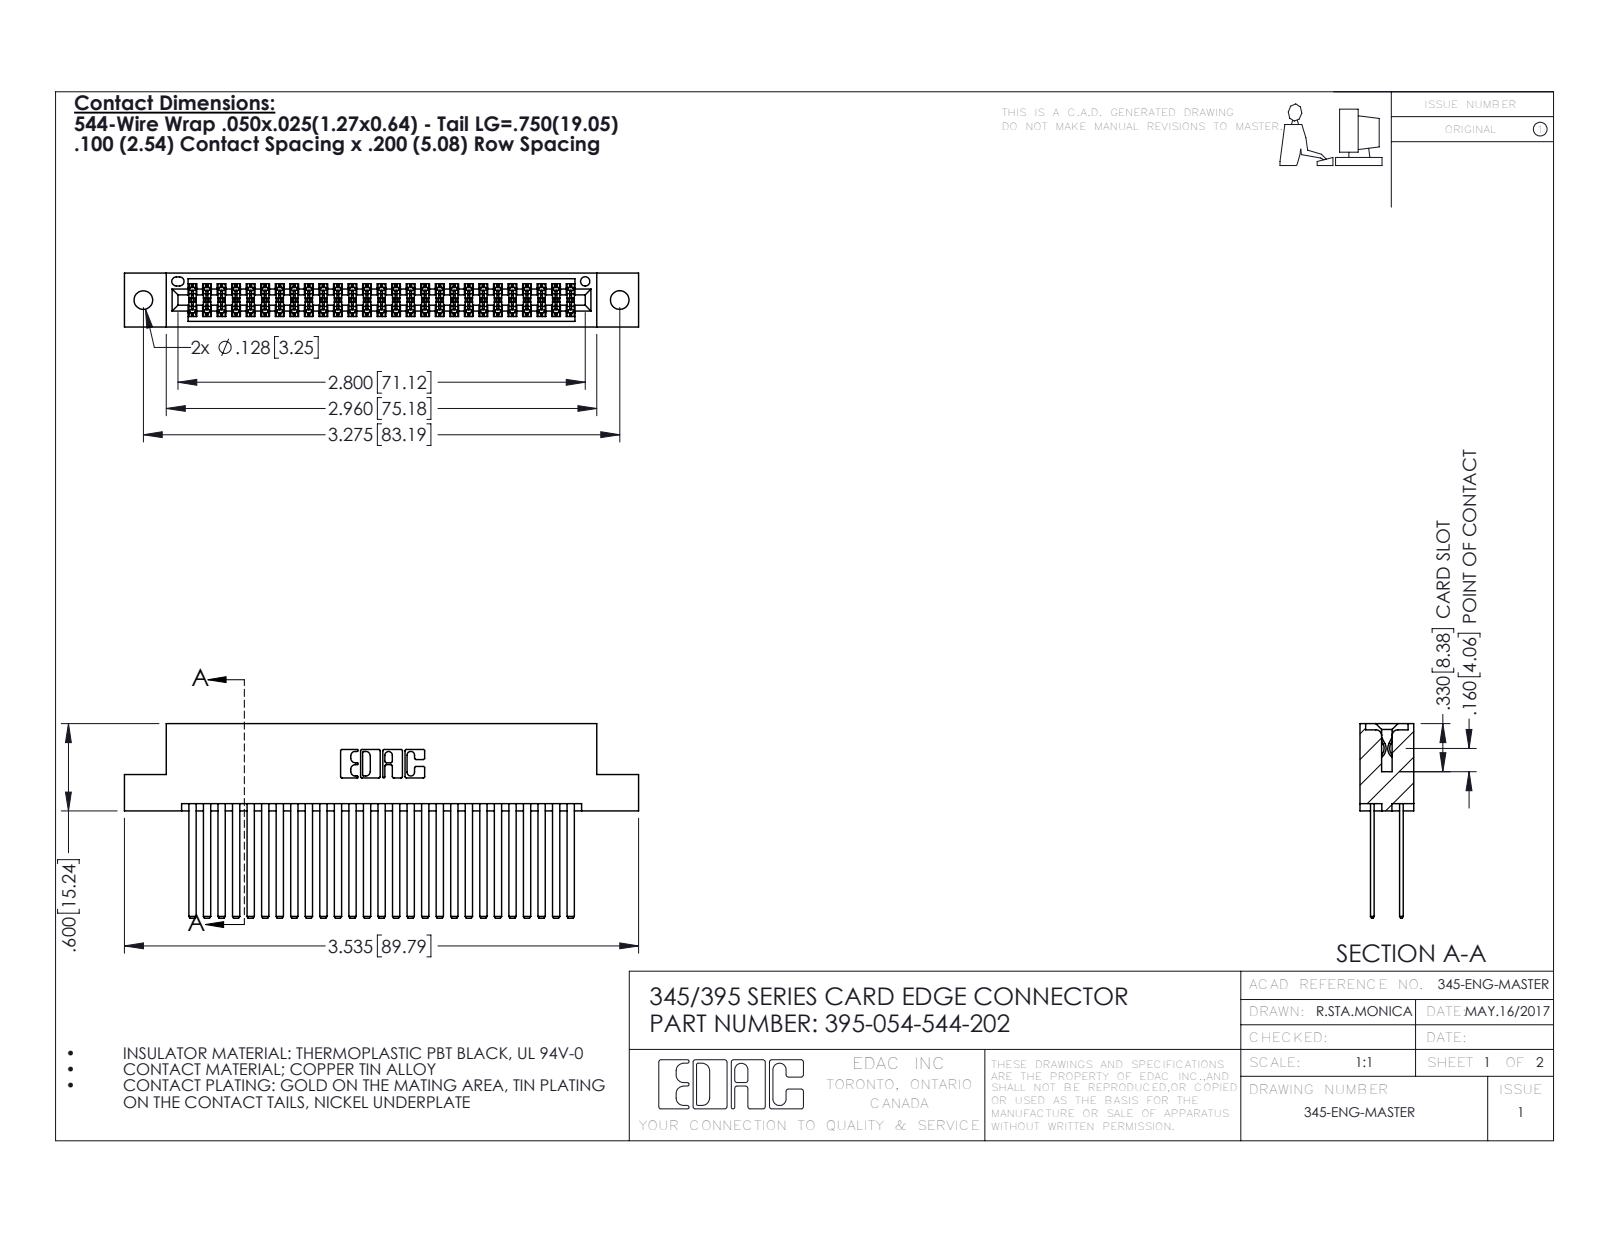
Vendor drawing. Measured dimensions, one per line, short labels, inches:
name: 345 Part_Flush Mounting Lugs - 0.128 Dia; 395-054-544-202; 345-292-001_345-293-144
written by: SolidWorks 2016 (CONFIG_CONTROL_DESIGN)
unit: in
bodies: 55 solids, 2502 faces (1646 planar, 856 cylindrical, 0 other)
size: 3.535 × 1.337 × 0.37
volume: 0.568 in³; area: 23.88 in²
holes: 2× ⌀0.128, 1× ⌀0.064
rounds: 81× R0.006, 22× R0.01, 6× R0.007, 6× R0.031, 3× R0.026, 2× R0.014, 2× R0.019, 2× R0.022
face distances: 0.2, 0.298, 0.072, 0.025, 0.098, 0.272, 0.225, 0.175, 0.37, 0.05
hole spacings: 0.27, 3.04, 3.275
